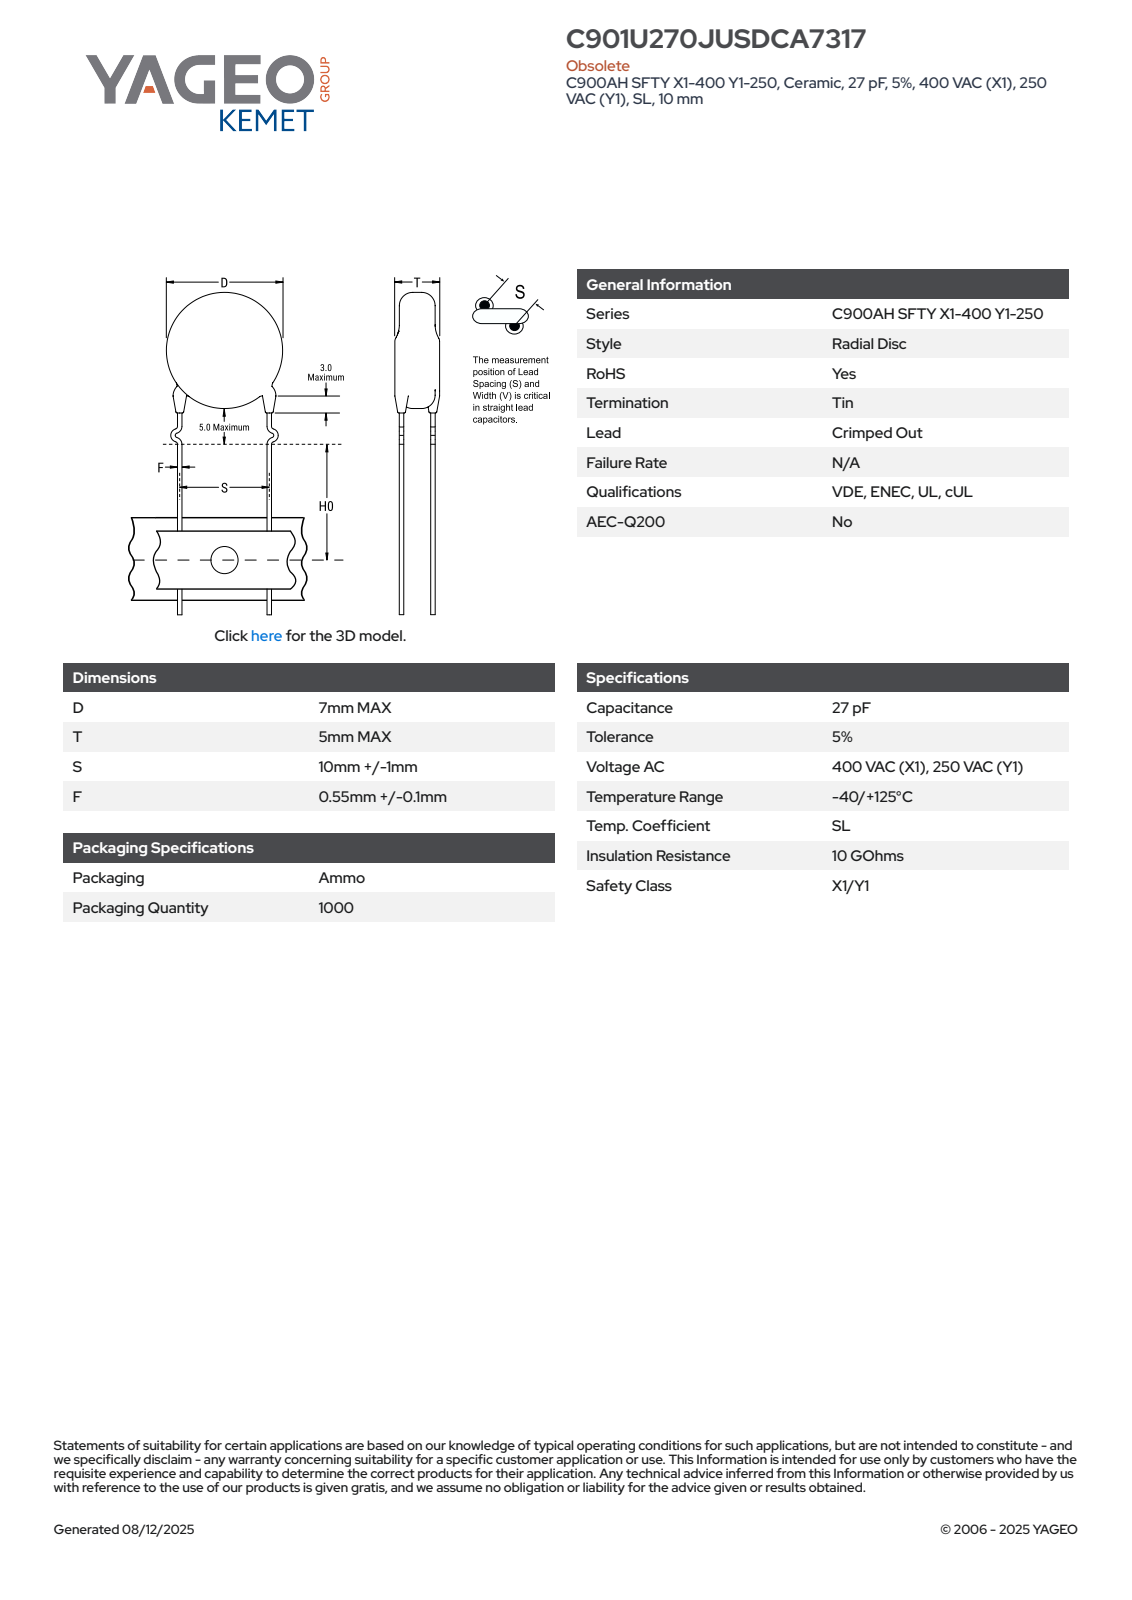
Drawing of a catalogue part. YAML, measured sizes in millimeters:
part_name: "CCD_KCOC900_D7T5S10LL20F0.55"
step_written_by: "SolidWorks 2014 (AUTOMOTIVE_DESIGN)"
units: millimeters
bodies: {solids: 4, faces: 93, planar: 63, cylindrical: 10, other: 20}
overall_size: [32, 13.89, 6.87]
volume: 209
surface_area: 306
round_bosses_or_shafts:
  - {diameter: 1.2, count: 4}
  - {diameter: 7, count: 1}
face_to_face_distances: [5, 0.73, 3.87, 3.14, 0.59, 0.32, 2.97, 1.5, 2.16, 2.24]
